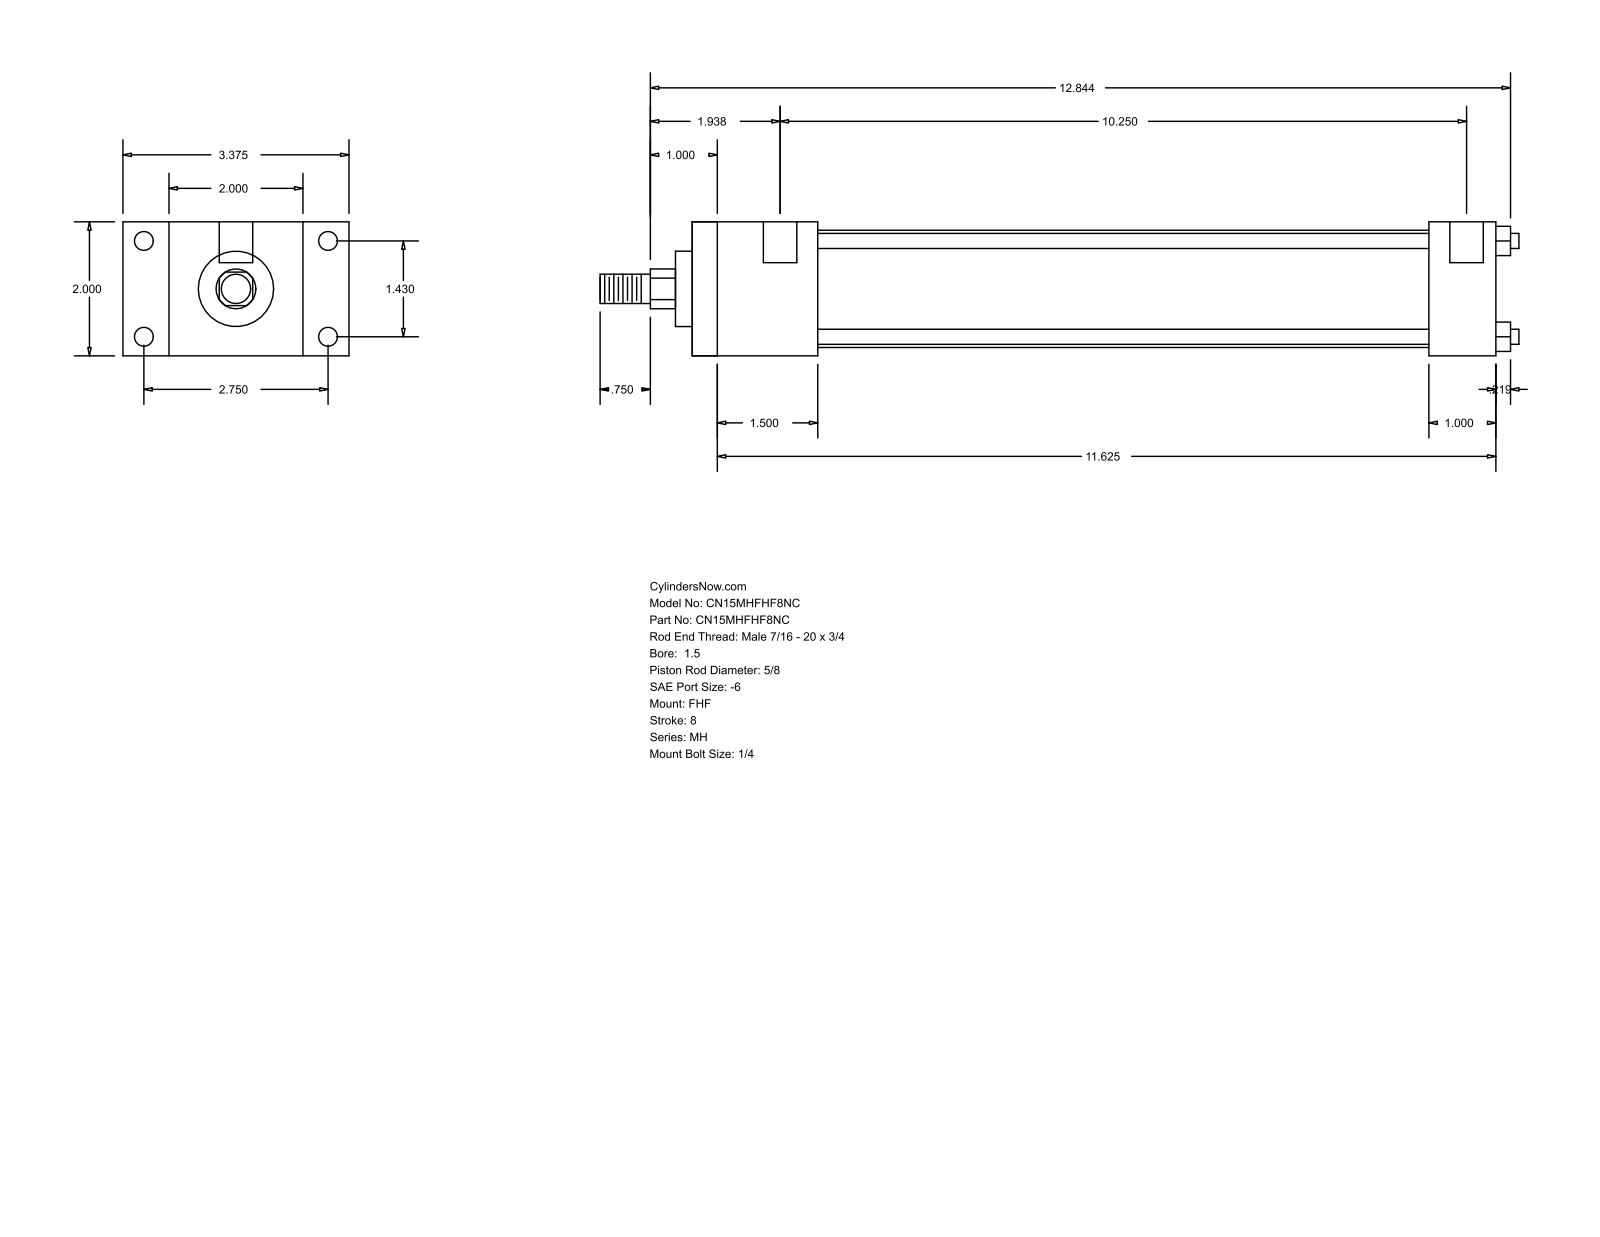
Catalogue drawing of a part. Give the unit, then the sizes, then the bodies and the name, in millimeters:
Units: millimetres
Overall size (bounding box): 348.46 × 85.72 × 50.8
Round holes (diameter × count): ⌀5.56 ×4, ⌀7.14 ×4, ⌀12.7 ×2
Round bosses / shafts (diameter × count): ⌀5.71 ×4, ⌀44.45 ×1, ⌀28.57 ×1, ⌀15.88 ×1, ⌀11.11 ×1
Partial cylindrical surfaces — rounded edges, fillets, slot ends (radius × count): R7.54 ×1
Main face-to-face distances: 50.8, 17.46, 68.26, 47.62, 85.72, 304.8, 257.18, 279.39, 231.77, 25.41
Hole centre spacings: 36.32, 69.84, 78.72, 263.52, 3.17, 260.35
Bodies: 0 solids, 88 faces (60 planar, 28 cylindrical, 0 other)
Part name (STEP PRODUCT): MH_FHF__0150_0.625
STEP written by: GSSL Pune (CONFIG_CONTROL_DESIGN)
